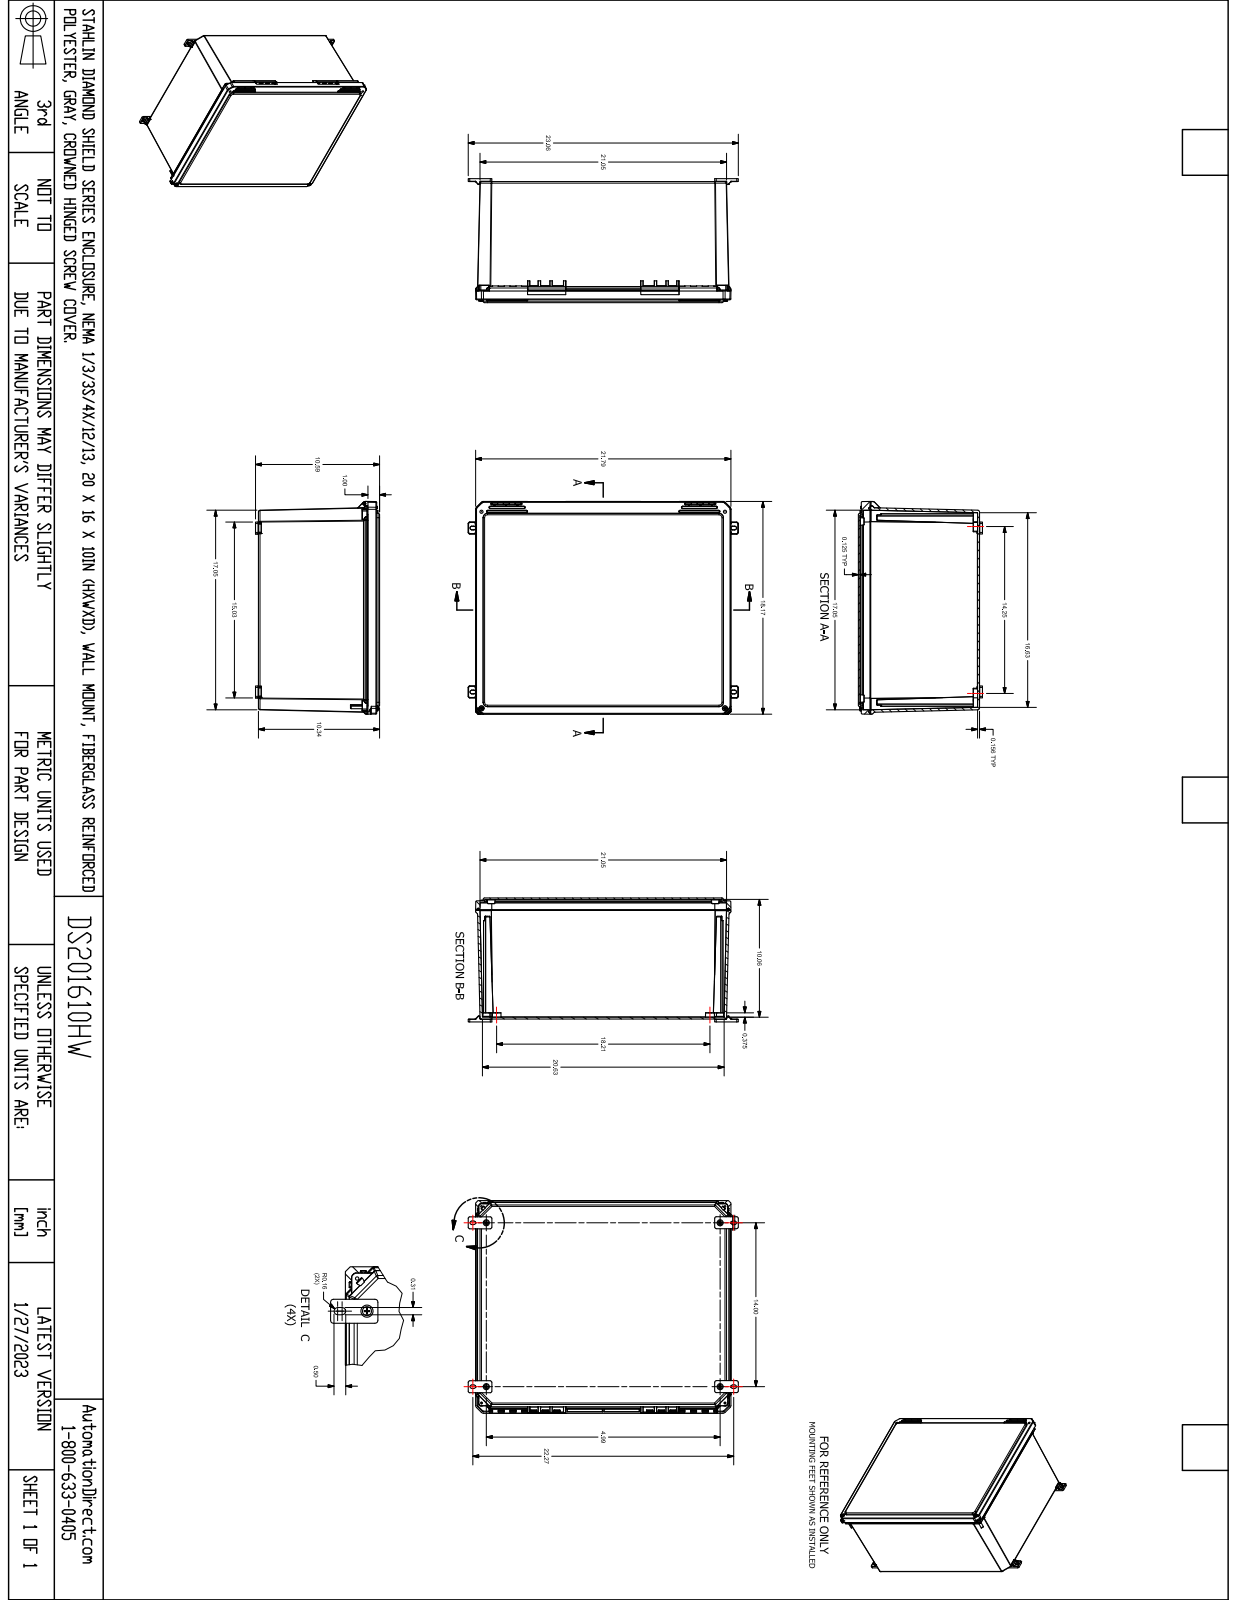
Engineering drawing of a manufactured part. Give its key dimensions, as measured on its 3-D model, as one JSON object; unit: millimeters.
{"part_name": "FR201610HW", "step_written_by": "SolidWorks 2021 (AUTOMOTIVE_DESIGN)", "units": "millimeters", "bodies": {"solids": 23, "faces": 2239, "planar": 704, "cylindrical": 890, "other": 645}, "overall_size": [553.6, 461.7, 277.2], "volume_mm3": 4667000, "surface_area_mm2": 2049000, "round_holes": [[3.9, 8], [4, 8], [4, 4], [6.4, 4], [6.4, 4], [3.5, 3], [3.8, 2], [5.6, 2], [5.8, 2], [8, 2]], "round_bosses_or_shafts": [[6.9, 8], [6.7, 4], [11.4, 2], [5.3, 2], [5.1, 2], [3.4, 2], [11, 1], [11, 1]], "partial_cylinders_radius": [[0.3, 190], [0.1, 110], [0.5, 54], [0.8, 51], [0.8, 24], [2.3, 24], [2.4, 24], [3.2, 22]], "face_to_face_distances": [3.2, 4, 258.6, 262.6, 255.4, 259.4, 5.4, 5.3, 5.3, 6.4], "hole_center_spacings": [496.8, 518.7, 359.4, 507.5, 528, 528.1, 21.9, 395.5]}
